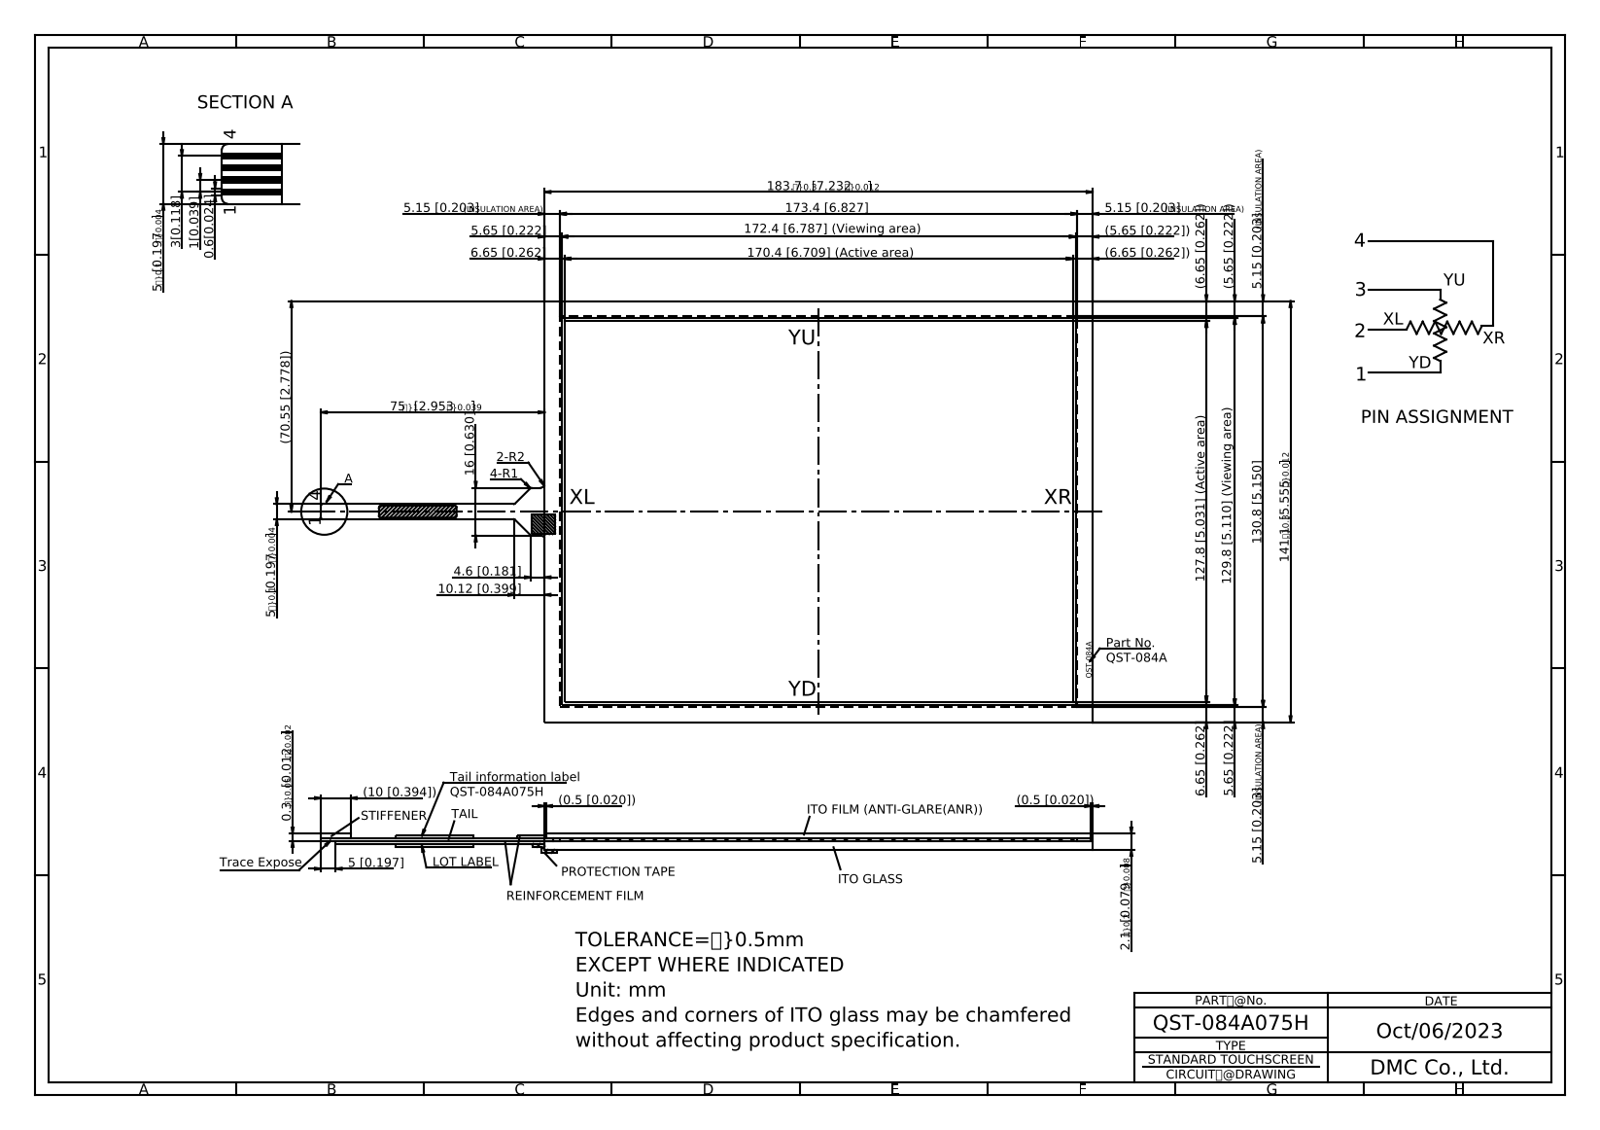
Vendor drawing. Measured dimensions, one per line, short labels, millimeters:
name: QST-084A075H
written by: Autodesk Inventor 2020 (CONFIG_CONTROL_DESIGN)
unit: mm
bodies: 1 solid, 51 faces (45 planar, 6 cylindrical, 0 other)
size: 295.44 × 197.54 × 2.2
volume: 54 430 mm³; area: 54 258 mm²
rounds: 2× R0.5, 2× R1, 2× R2
face distances: 2.1, 2, 1.8, 1.9, 141.1, 183.7, 5.65, 1, 6.65, 0.4
